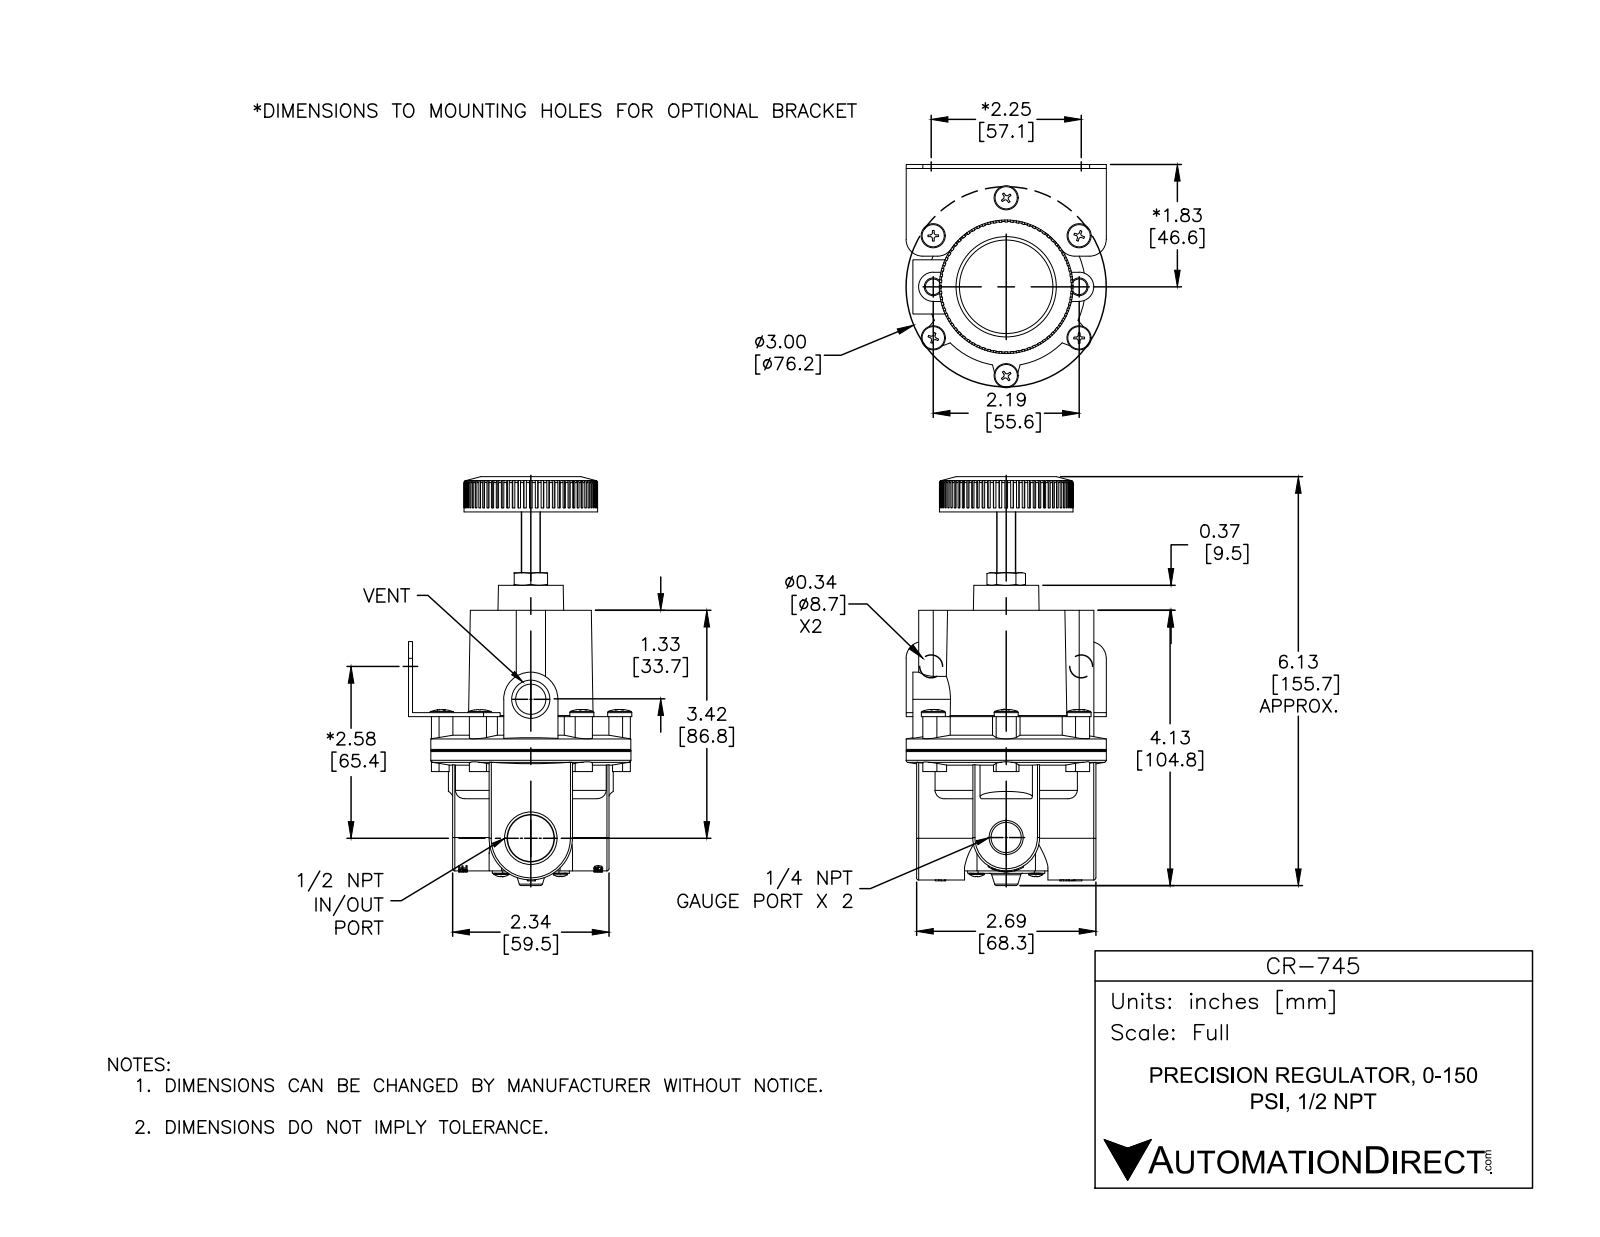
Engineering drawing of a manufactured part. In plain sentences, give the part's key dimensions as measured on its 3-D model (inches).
The part is named "CR-745". Its 3-D file was written by "SolidWorks 2015 (CONFIG_CONTROL_DESIGN)". It is 10 solids with 1525 faces: 521 planar, 817 cylindrical and 187 other. Overall it measures 6.123 by 3.041 by 3 inches. Its volume is 17.07 cubic inches and its surface area 89.38 square inches. Round holes: 8 of diameter 0.201, 6 of diameter 0.159, 2 of diameter 0.438, 1 of diameter 0.703, 1 of diameter 1.403, 1 of diameter 1.683. Round bosses or shafts: 6 of diameter 0.373, 6 of diameter 0.19, 6 of diameter 0.149, 1 of diameter 3, 1 of diameter 2, 1 of diameter 0.628, 1 of diameter 0.281. Partial cylindrical surfaces (rounded edges, fillets, slot ends): 72 of radius 0.004, 18 of radius 0.02, 6 of radius 0.032, 6 of radius 0.156, 6 of radius 0.157, 4 of radius 0.141, 3 of radius 0.187, 2 of radius 0.033. The main face-to-face distances are 0.034, 2.114, 2.08, 0.524, 0.49, 1.59, 3.879, 3.845, 3.355, 1.765. The hole center spacings are 1.334, 1.725, 2.317, 0.765, 0.765, 1.094, 1.232, 1.232.
